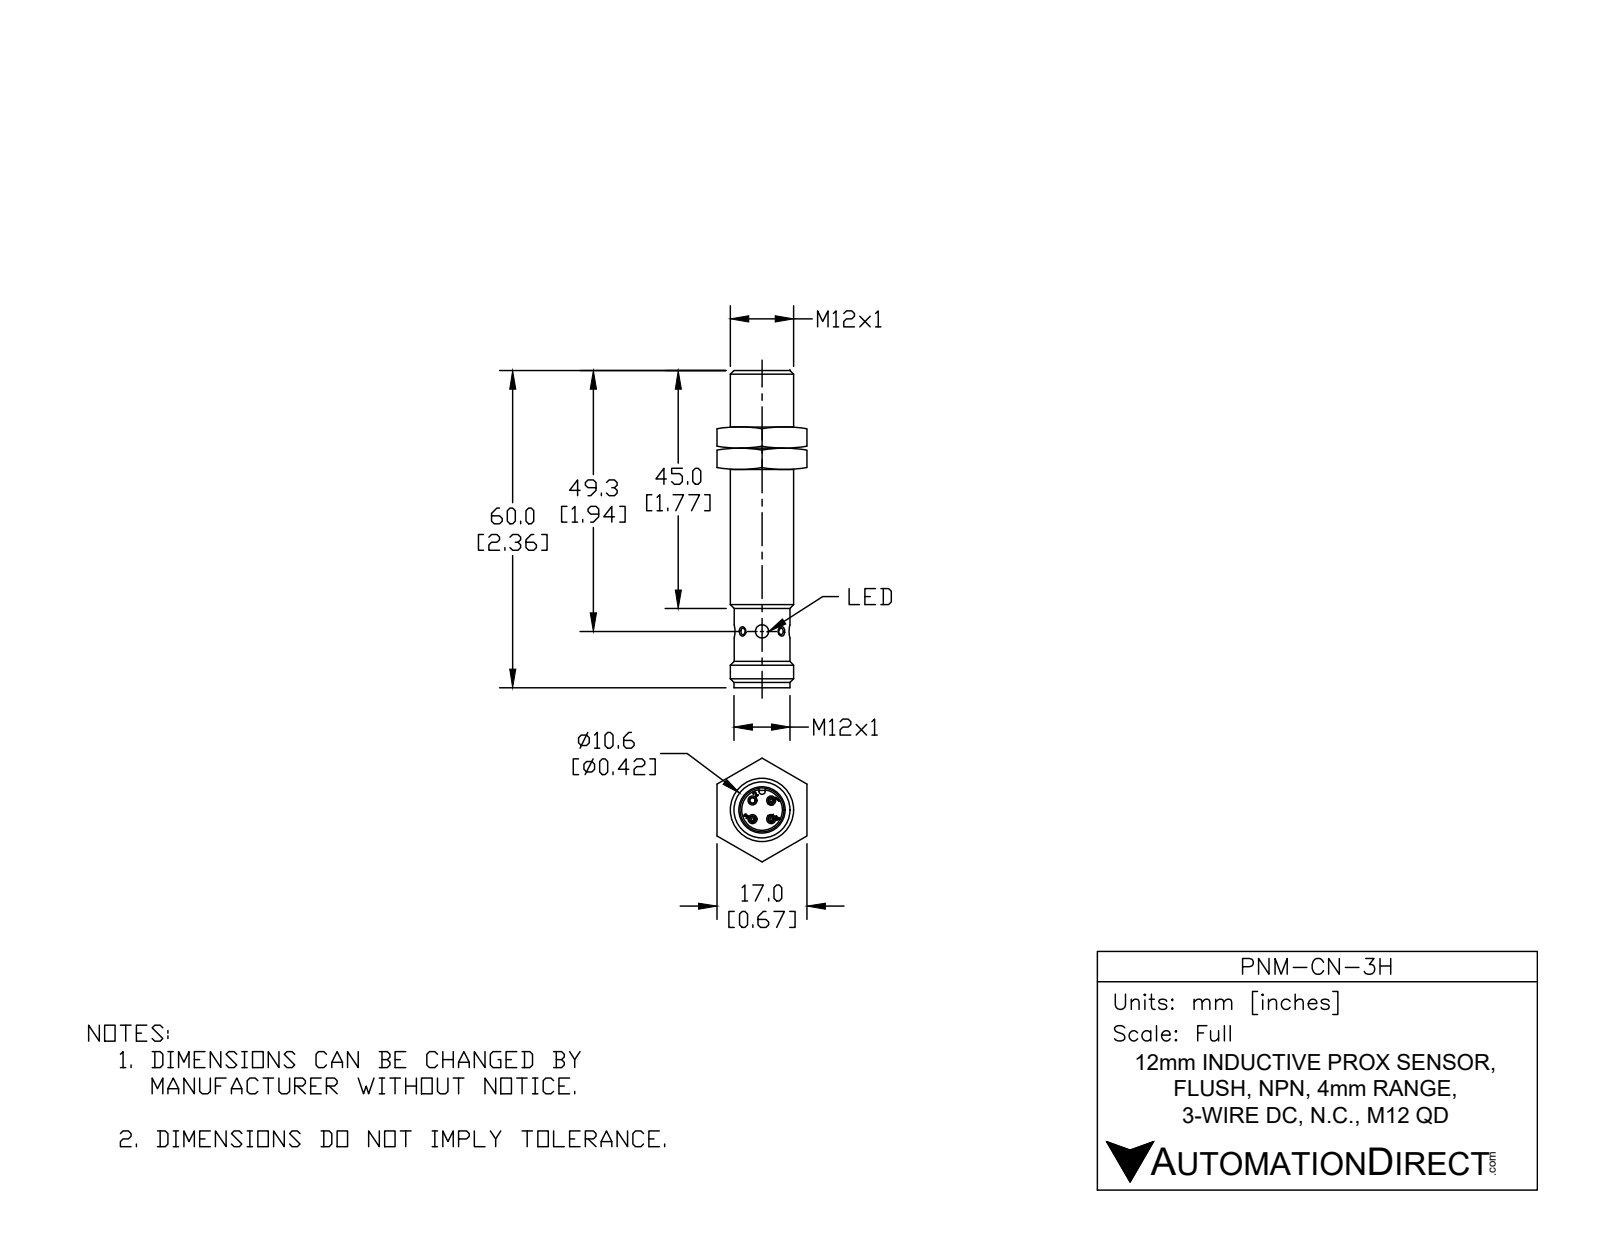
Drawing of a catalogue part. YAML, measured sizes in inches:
part_name: "PNM-CN-3H"
step_written_by: "SolidWorks 2017 (AUTOMOTIVE_DESIGN)"
units: inches
bodies: {solids: 1, faces: 479, planar: 119, cylindrical: 134, other: 226}
overall_size: [2.362, 0.472, 0.472]
volume: 0.35
surface_area: 10.25
round_holes:
  - {diameter: 0.043, count: 3}
  - {diameter: 0.04, count: 2}
  - {diameter: 0.098, count: 2}
  - {diameter: 0.038, count: 1}
  - {diameter: 0.04, count: 1}
  - {diameter: 0.327, count: 1}
  - {diameter: 0.394, count: 1}
  - {diameter: 0.401, count: 1}
round_bosses_or_shafts:
  - {diameter: 0.039, count: 9}
  - {diameter: 0.472, count: 1}
  - {diameter: 0.417, count: 1}
  - {diameter: 0.415, count: 1}
  - {diameter: 0.4, count: 1}
  - {diameter: 0.392, count: 1}
  - {diameter: 0.39, count: 1}
  - {diameter: 0.376, count: 1}
partial_cylinders:
  - {radius: 0.004, count: 36}
  - {radius: 0.024, count: 1}
  - {radius: 0.031, count: 1}
  - {radius: 0.161, count: 1}
face_to_face_distances: [0.039, 1.87, 1.831, 0.018, 0.022, 1.852, 2.323, 0.142, 2.012, 1.994]
hole_center_spacings: [0.098, 0.139, 0.197]
